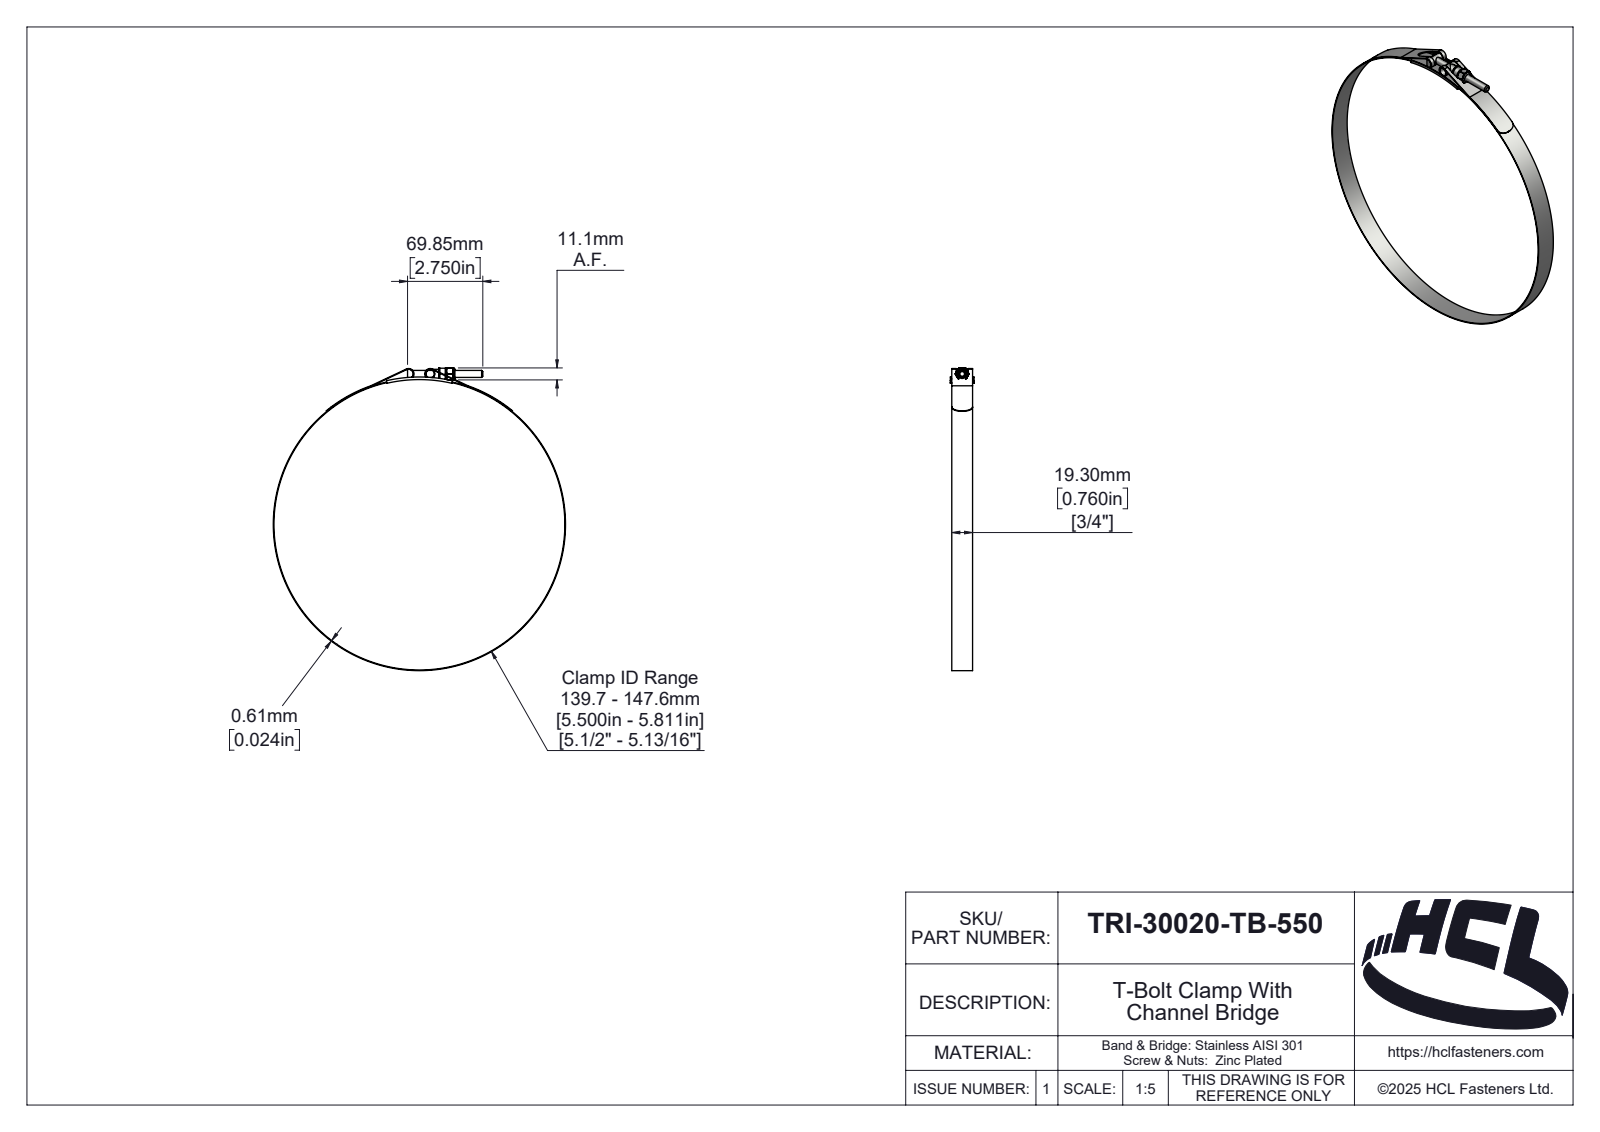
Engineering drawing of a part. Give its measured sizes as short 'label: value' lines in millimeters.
name: TRI-30020-TB-550
written by: SolidWorks 2025 (AUTOMOTIVE_DESIGN)
unit: mm
bodies: 6 solids, 330 faces (44 planar, 122 cylindrical, 164 other)
size: 280.97 × 271.22 × 22
volume: 16 826 mm³; area: 47 269 mm²
holes: 1× ⌀5.4, 1× ⌀6.35, 1× ⌀6.5, 1× ⌀7.58, 1× ⌀270
bosses: 2× ⌀8.58, 1× ⌀271.22, 1× ⌀10.58
rounds: 6× R0.39, 2× R0.5, 2× R4.39, 2× R5, 1× R0.59, 1× R2.42, 1× R3.03, 1× R3.19
face distances: 0.61, 19.3, 1.35, 20.65, 0.74, 21.39, 20.04, 22, 20.78, 11.11
hole spacings: 140
